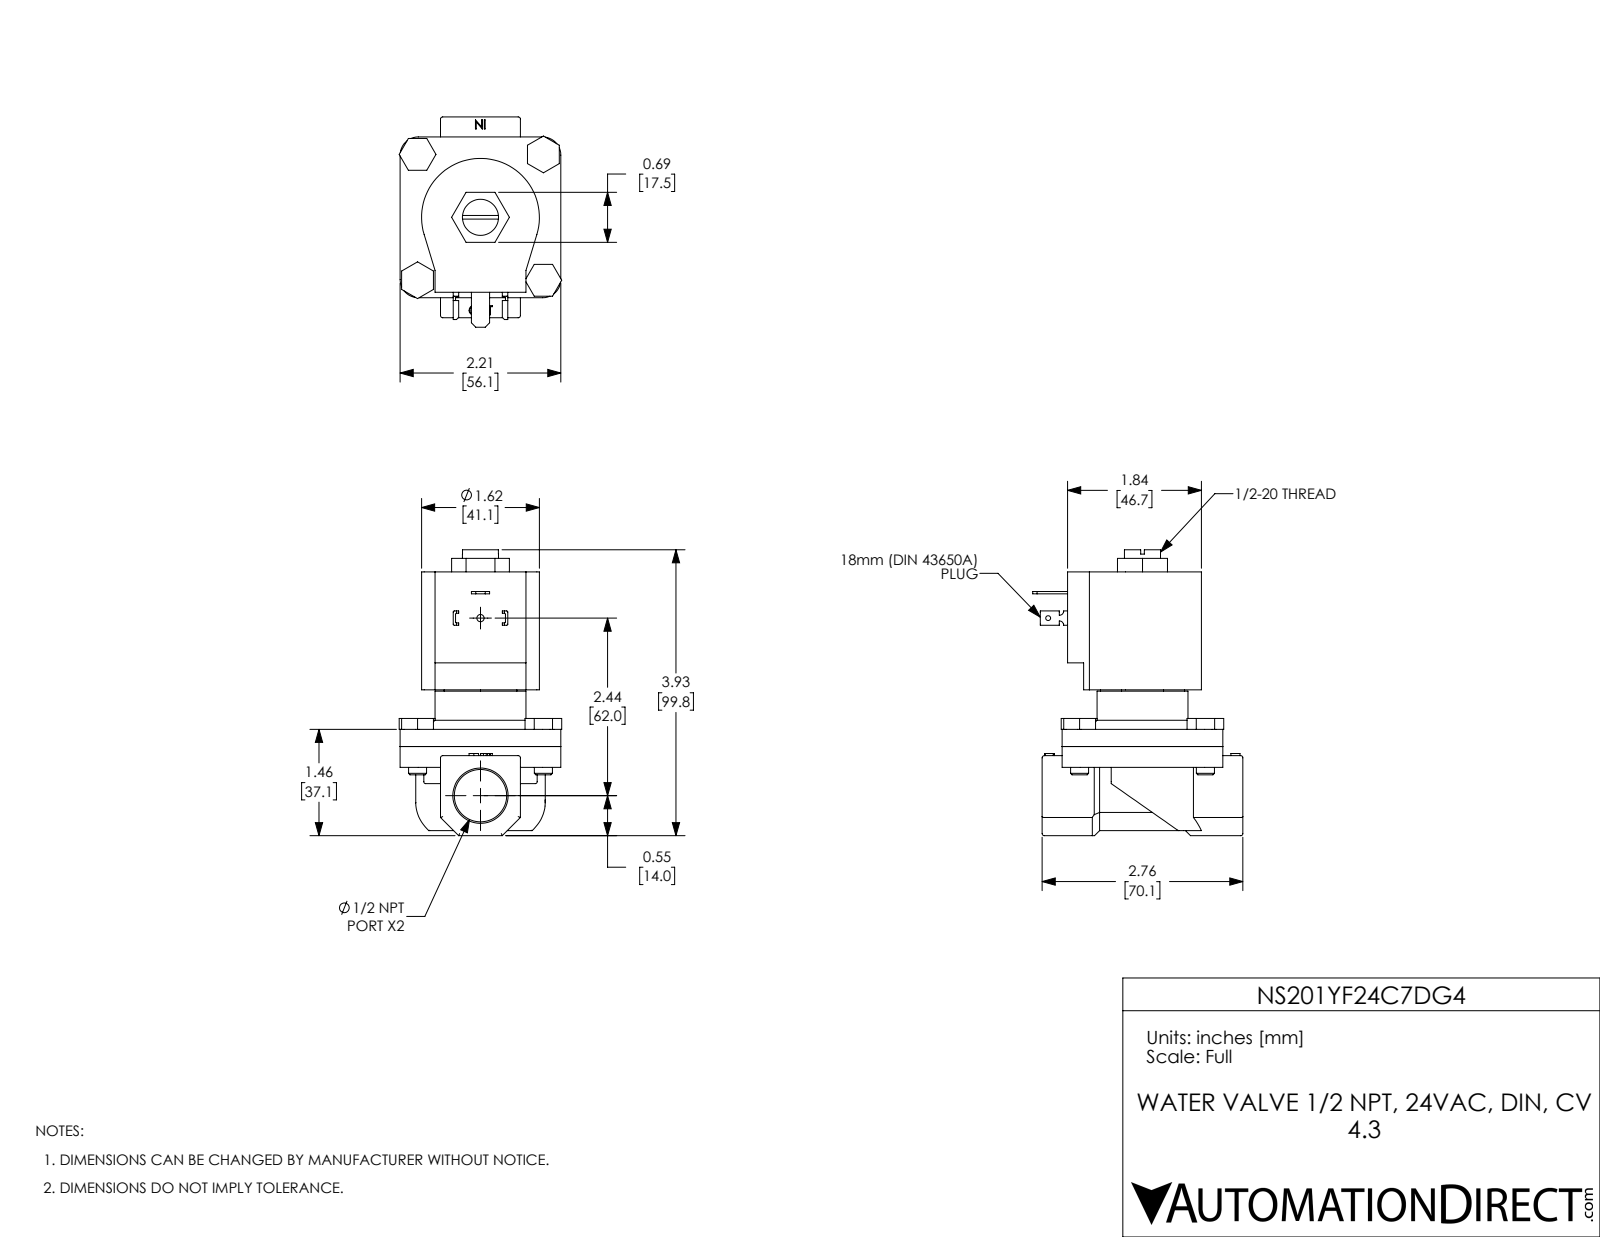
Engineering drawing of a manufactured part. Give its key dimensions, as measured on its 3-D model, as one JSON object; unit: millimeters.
{"part_name": "NS201YF24C7DG4", "step_written_by": "SolidWorks 2021 (CONFIG_CONTROL_DESIGN)", "units": "millimeters", "bodies": {"solids": 11, "faces": 330, "planar": 196, "cylindrical": 99, "other": 35}, "overall_size": [99.8, 73.4, 56.8], "volume_mm3": 160900, "surface_area_mm2": 40930, "round_holes": [[6.4, 4], [1.7, 1], [2.5, 1], [12.6, 1], [13, 1], [18.3, 1], [29.3, 1]], "round_bosses_or_shafts": [[6.3, 4], [31.8, 1]], "partial_cylinders_radius": [[0.8, 15], [0.4, 8], [6.4, 4], [1.5, 2], [20.6, 1], [22.6, 1]], "face_to_face_distances": [6, 6, 61, 61, 54.9, 14.1, 42, 7.3, 7.3, 13.3], "hole_center_spacings": [31.1, 43.9, 62.1, 62]}
